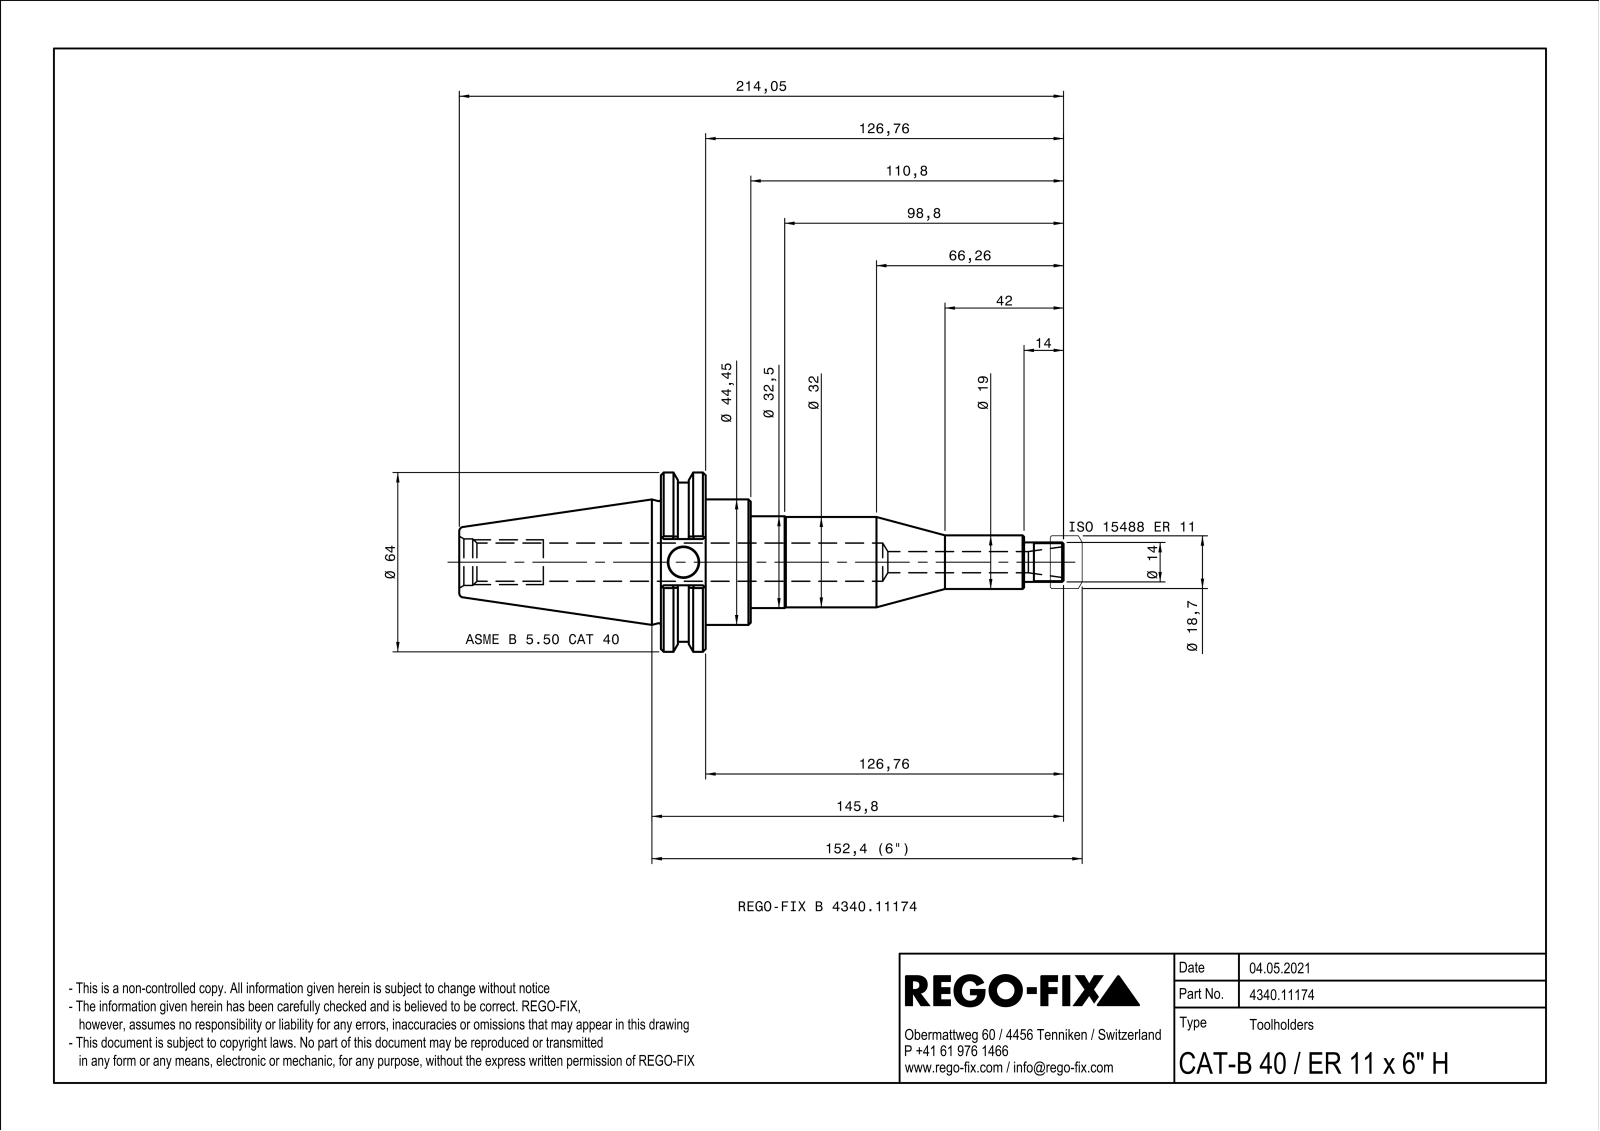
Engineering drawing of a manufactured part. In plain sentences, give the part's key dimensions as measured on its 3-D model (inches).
The part is named "NOCUT". Its 3-D file was written by "SIEMENS PLM Software Solid Edge ST10 (AUTOMOTIVE_DESIGN)". It is 1 solid with 117 faces: 32 planar, 34 cylindrical and 51 other. Overall it measures 8.427 by 2.5 by 2.393 inches. Its volume is 10.39 cubic inches and its surface area 55.23 square inches. Round holes: 2 of diameter 0.128, 2 of diameter 0.154, 1 of diameter 0.295, 1 of diameter 0.421, 1 of diameter 0.533, 1 of diameter 0.65. Round bosses or shafts: 1 of diameter 2.5, 1 of diameter 2.219, 1 of diameter 1.75, 1 of diameter 1.28, 1 of diameter 1.26, 1 of diameter 0.748, 1 of diameter 0.551. Partial cylindrical surfaces (rounded edges, fillets, slot ends): 4 of radius 0.02. The main face-to-face distances are 0.625, 0.628, 1.253, 1.863, 0.645, 4.065, 3.437, 2.812, 0.864, 0.236.
